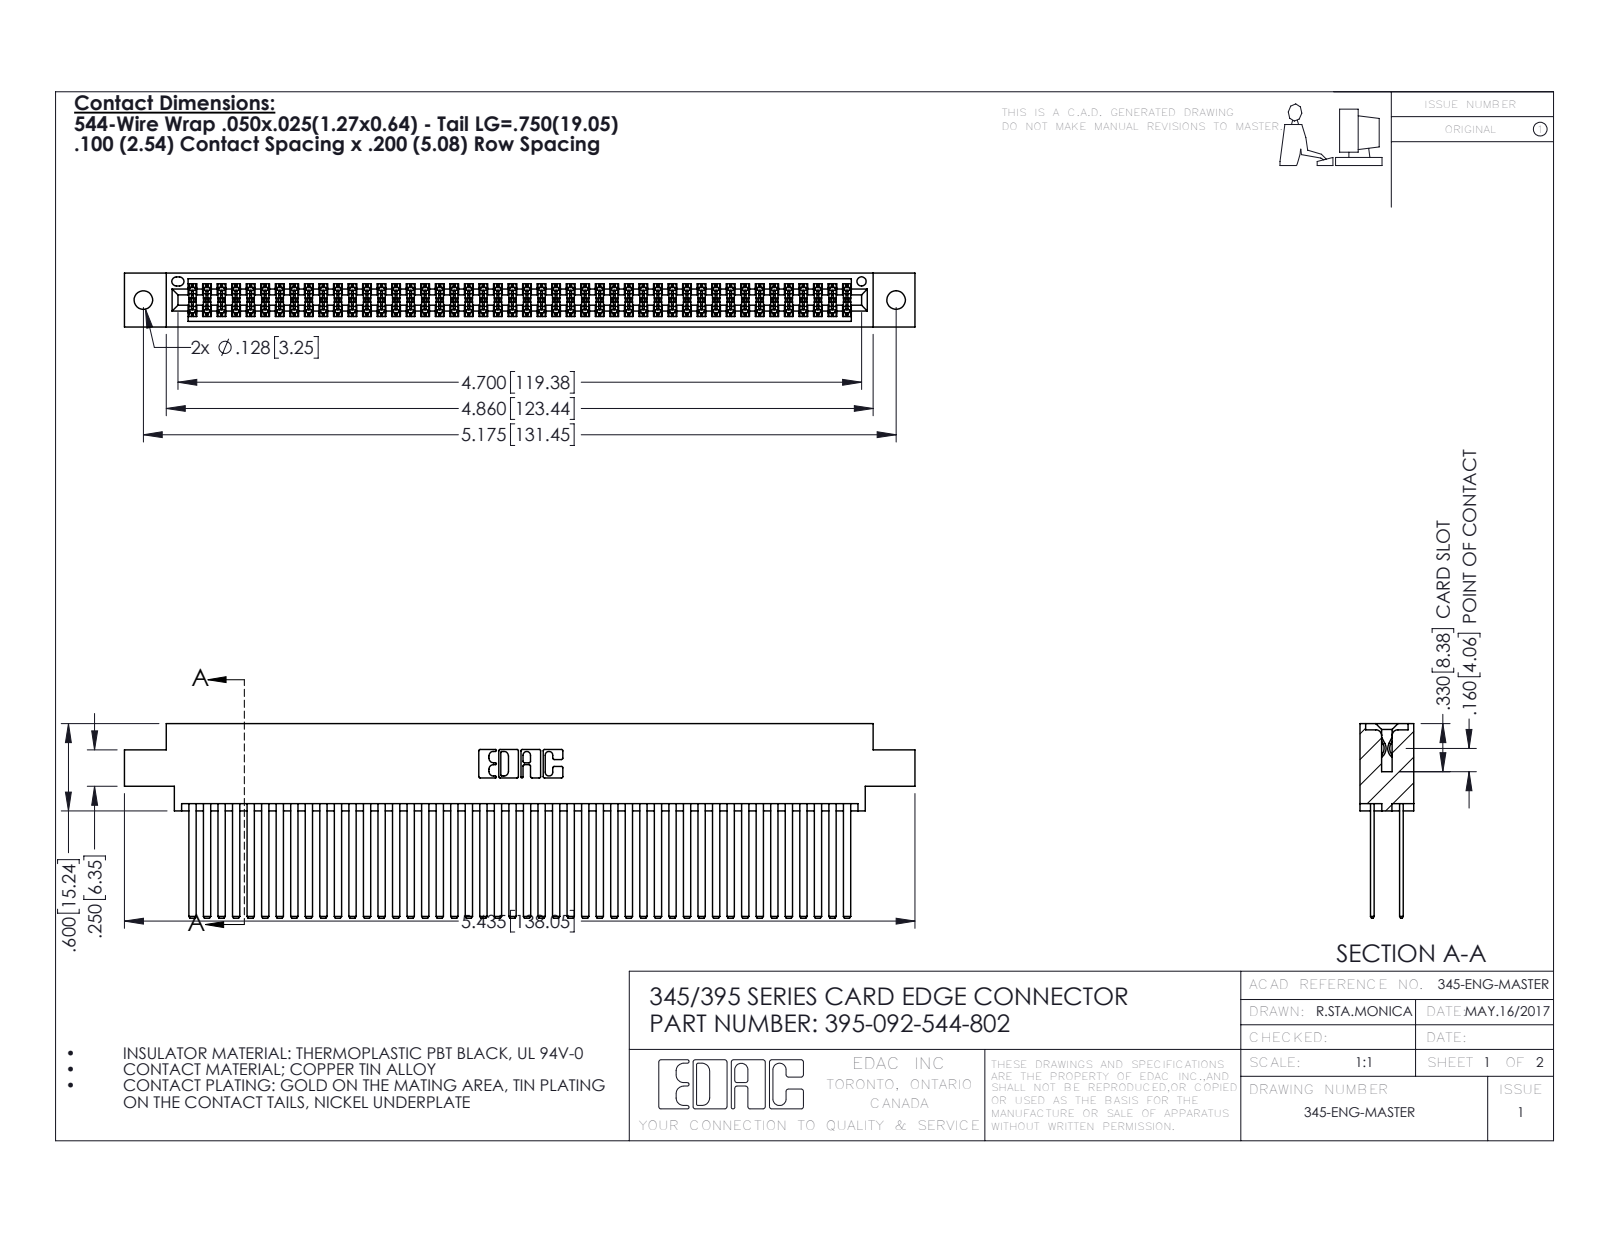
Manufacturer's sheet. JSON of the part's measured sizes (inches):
{"part_name": "345 Part_0.170 Offset - 0.128 Dia; 345-292-001_345-293-144; 395-092-544-802", "step_written_by": "SolidWorks 2016 (CONFIG_CONTROL_DESIGN)", "units": "inches", "bodies": {"solids": 93, "faces": 4178, "planar": 2752, "cylindrical": 1426, "other": 0}, "overall_size": [5.435, 1.337, 0.37], "volume_in3": 0.89, "surface_area_in2": 39.2, "round_holes": [[0.128, 2], [0.064, 1]], "partial_cylinders_radius": [[0.006, 138], [0.01, 22], [0.007, 6], [0.031, 6], [0.026, 3], [0.014, 2], [0.019, 2], [0.022, 2]], "face_to_face_distances": [0.2, 0.025, 0.072, 0.098, 0.272, 0.298, 0.225, 0.175, 0.37, 0.15], "hole_center_spacings": [0.27, 4.939, 5.175]}
